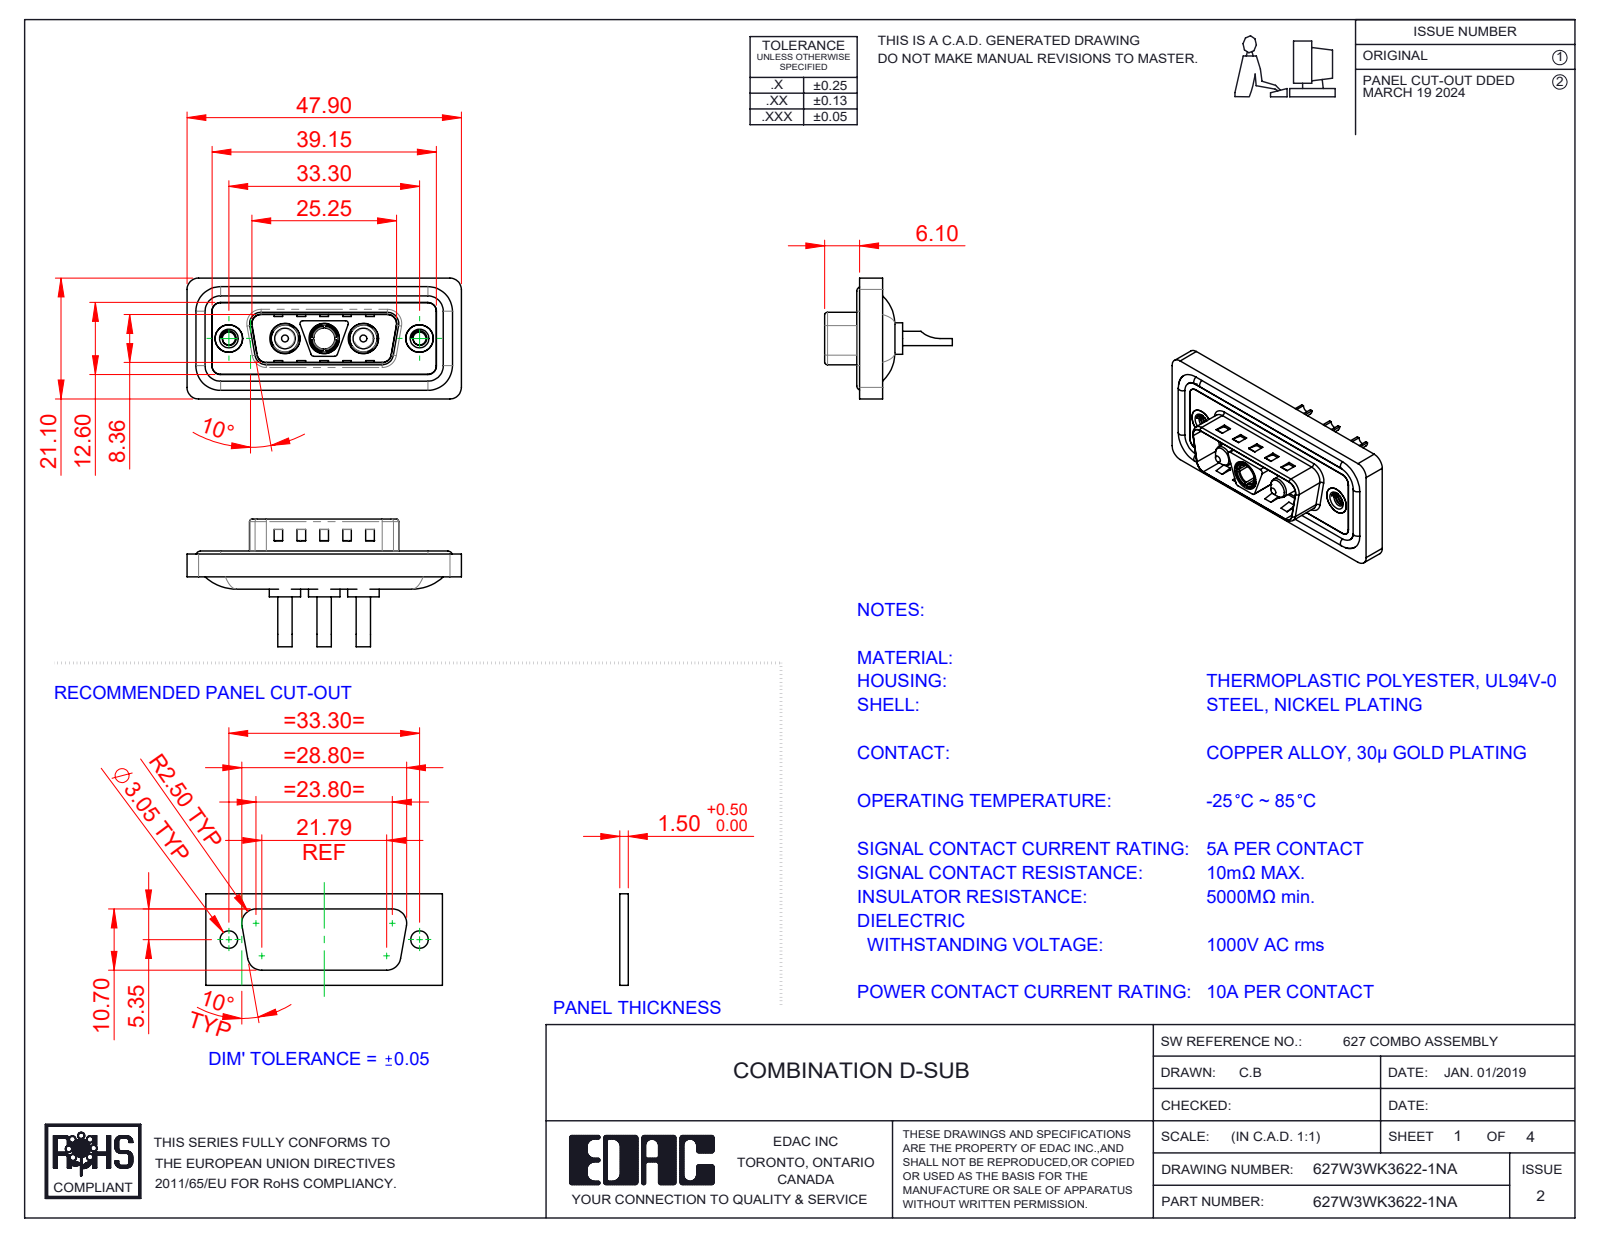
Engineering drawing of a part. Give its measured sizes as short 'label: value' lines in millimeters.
name: 627Combo Shell Rear_15 Contacts; 627Combo Housing_3WK3; 627Combo Threaded Rivet_A; 627Combo Waterproof Housing_15 Contacts (+4 more)
written by: SolidWorks 2023 (CONFIG_CONTROL_DESIGN)
unit: mm
bodies: 13 solids, 625 faces (237 planar, 261 cylindrical, 127 other)
size: 47.9 × 22.3 × 21.1
volume: 5 681 mm³; area: 9 268 mm²
holes: 3× ⌀1.7, 3× ⌀4.85, 3× ⌀5.3, 2× ⌀2.26, 2× ⌀4, 2× ⌀4.8, 2× ⌀5, 1× ⌀3.7
bosses: 4× ⌀1.6, 3× ⌀5.5, 3× ⌀5.2, 3× ⌀4.75, 3× ⌀3.75, 3× ⌀2.5, 2× ⌀4.9, 2× ⌀3.6
rounds: 26× R1.5, 20× R2, 12× R0.5, 8× R1.6, 4× R0.25, 4× R0.6, 4× R0.65, 4× R0.9
face distances: 0.4, 1.1, 1.5, 0.5, 1.6, 3.1, 2.9, 4, 0.82, 9.58
hole spacings: 6.85, 9.8, 16.65, 23.5, 13.7, 33.3
